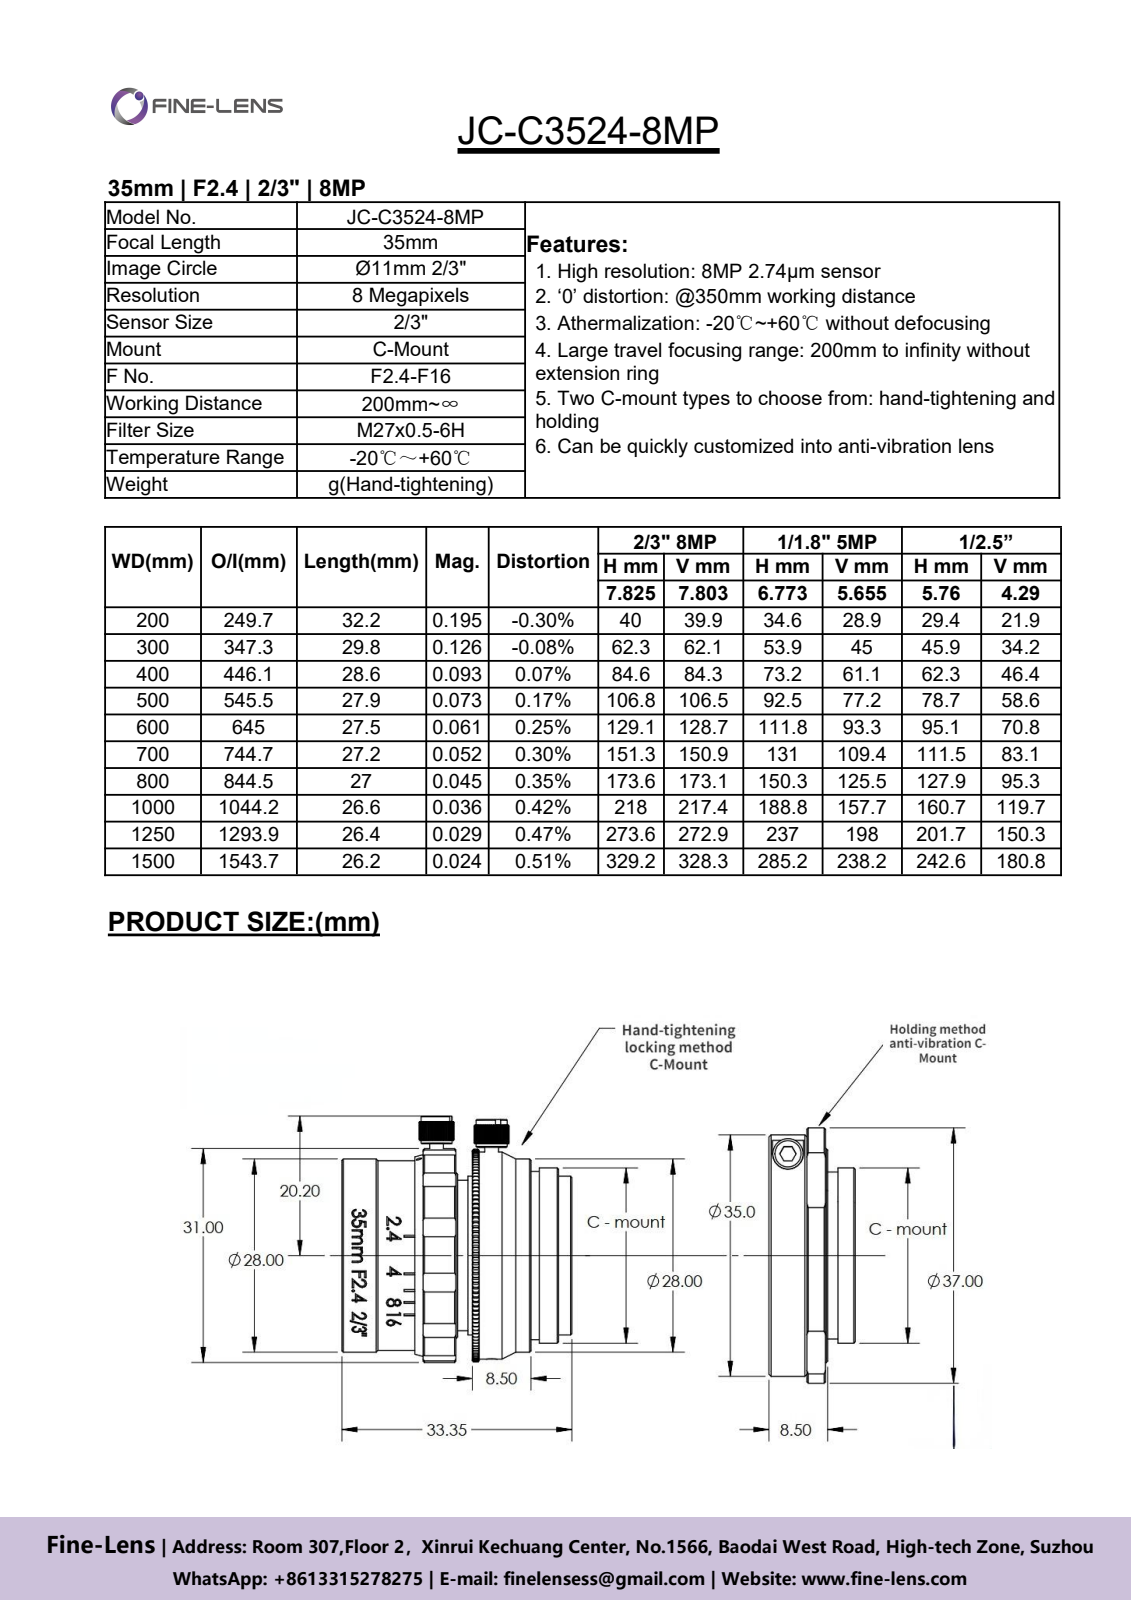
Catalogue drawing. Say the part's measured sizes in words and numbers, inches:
The part is named "2_3-3524 3D". Its 3-D file was written by "SolidWorks 2016 (CONFIG_CONTROL_DESIGN)". It is 5 solids with 1846 faces: 695 planar, 403 cylindrical and 748 other. Overall it measures 1.406 by 1.313 by 1.22 inches. Its volume is 0.618 cubic inches and its surface area 15.96 square inches. Round holes: 2 of diameter 0.063, 1 of diameter 0.031, 1 of diameter 0.643, 1 of diameter 0.728, 1 of diameter 0.756, 1 of diameter 0.807, 1 of diameter 0.882, 1 of diameter 0.969, 1 of diameter 1.043, 1 of diameter 1.071, 1 of diameter 1.087, 1 of diameter 1.142. Round bosses or shafts: 2 of diameter 0.177, 2 of diameter 0.079, 1 of diameter 1.181, 1 of diameter 1.102, 1 of diameter 1.083, 1 of diameter 1, 1 of diameter 0.961, 1 of diameter 0.945. Partial cylindrical surfaces (rounded edges, fillets, slot ends): 14 of radius 0.098, 1 of radius 0.039, 1 of radius 0.55, 1 of radius 0.606, 1 of radius 0.61. The main face-to-face distances are 0.635, 0.501, 0.134, 0.157, 0.303, 0.969, 0.469, 0.335, 0.331, 0.169. The hole center spacings are 0.315.
